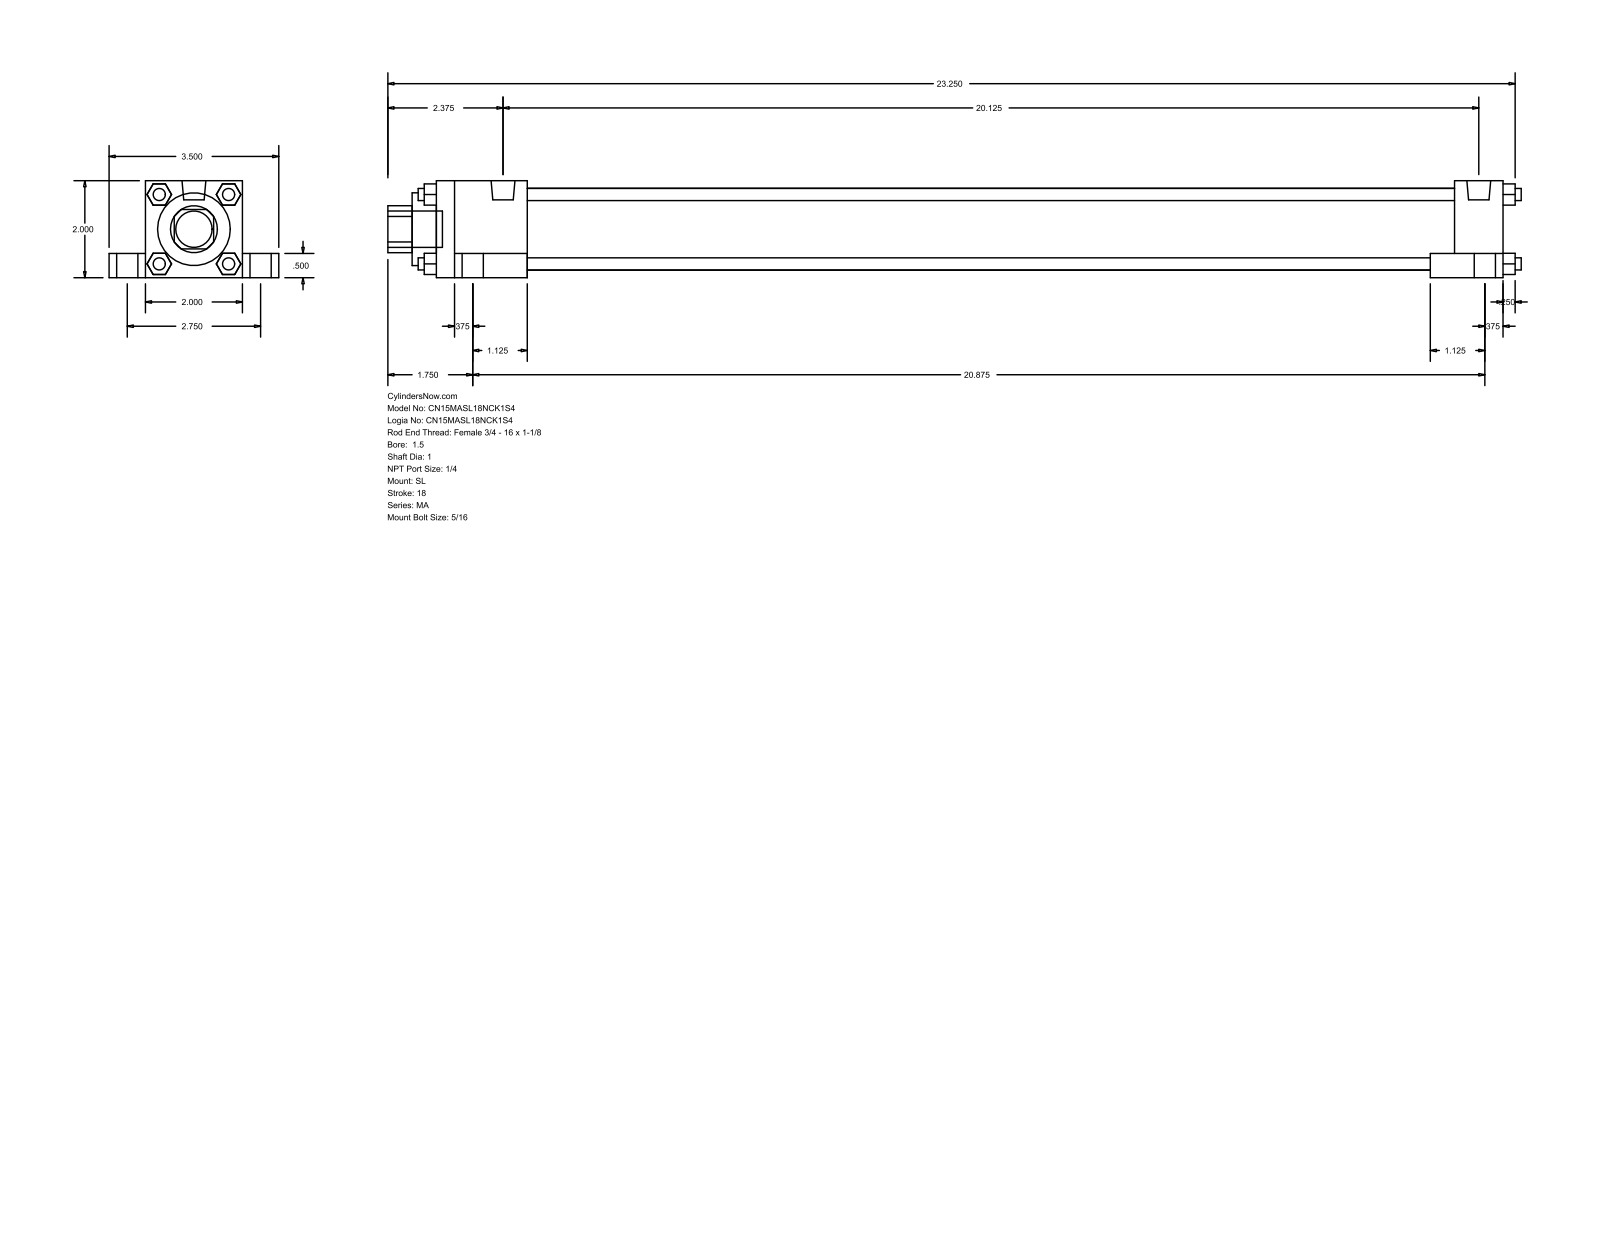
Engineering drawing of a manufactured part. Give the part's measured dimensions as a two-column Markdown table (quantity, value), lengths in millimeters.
| quantity | value |
| --- | --- |
| part name | MA_SL__0150_1 |
| STEP written by | GSSL Pune (CONFIG_CONTROL_DESIGN) |
| units | millimeters |
| bodies | 0 solids, 148 faces (112 planar, 36 cylindrical, 0 other) |
| overall size | 593.73 × 88.9 × 50.8 |
| round holes (diameter × count) | 25.4 × 1, 38.1 × 1, 42.93 × 1 |
| round bosses / shafts (diameter × count) | 17.46 × 4, 11.11 × 4, 7.94 × 4, 6.35 × 4, 12.49 × 2, 19.05 × 1 |
| partial cylindrical surfaces (radius × count) | 12.29 × 1 |
| main face-to-face distances | 50.8, 12.7, 19.05, 69.85, 9.52, 38.1, 6.35, 558.8, 25.4, 533.4 |
